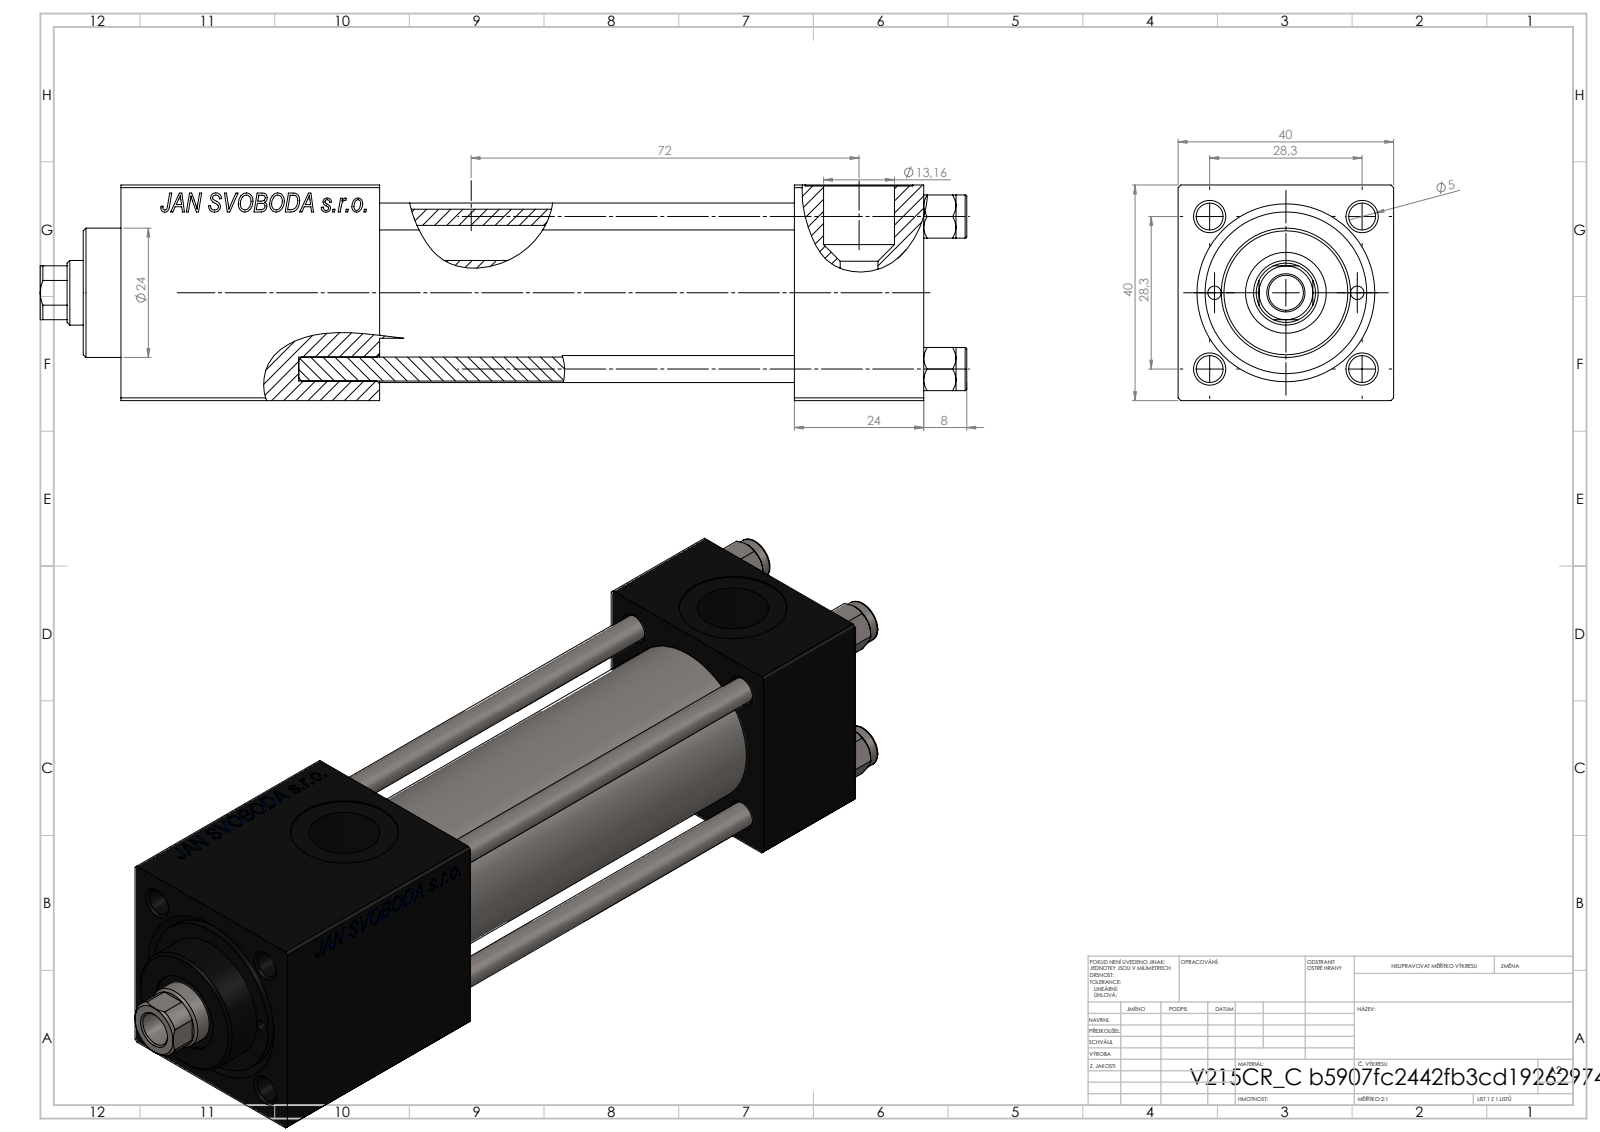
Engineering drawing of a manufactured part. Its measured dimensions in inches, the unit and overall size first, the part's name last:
Units: inches
Overall size (bounding box): 6.772 × 1.575 × 1.575
Round holes (diameter × count): ⌀0.197 ×4, ⌀0.787 ×3, ⌀0.098 ×2, ⌀0.276 ×2, ⌀0.518 ×2, ⌀0.256 ×1, ⌀0.472 ×1, ⌀0.591 ×1, ⌀0.984 ×1, ⌀1.181 ×1
Round bosses / shafts (diameter × count): ⌀0.315 ×4, ⌀1.22 ×1, ⌀0.945 ×1
Partial cylindrical surfaces — rounded edges, fillets, slot ends (radius × count): R0.217 ×1
Main face-to-face distances: 1.575, 0.945, 4.736, 3.791, 1.89, 3.976, 3.031, 0.76, 5.866, 4.921
Hole centre spacings: 0.558, 0.788, 1.114, 1.214, 0.522, 1.576, 1.043, 4.016
Volume: 9.515 in³ · Surface area: 97.36 in²
Bodies: 11 solids, 1154 faces (527 planar, 91 cylindrical, 536 other)
Part name (STEP PRODUCT): NUT_M5_C; V215_VC_A; V215CR_C_TYCINKA; V215CR_C_Body (+1 more)
STEP written by: SolidWorks 2019 (CONFIG_CONTROL_DESIGN)
